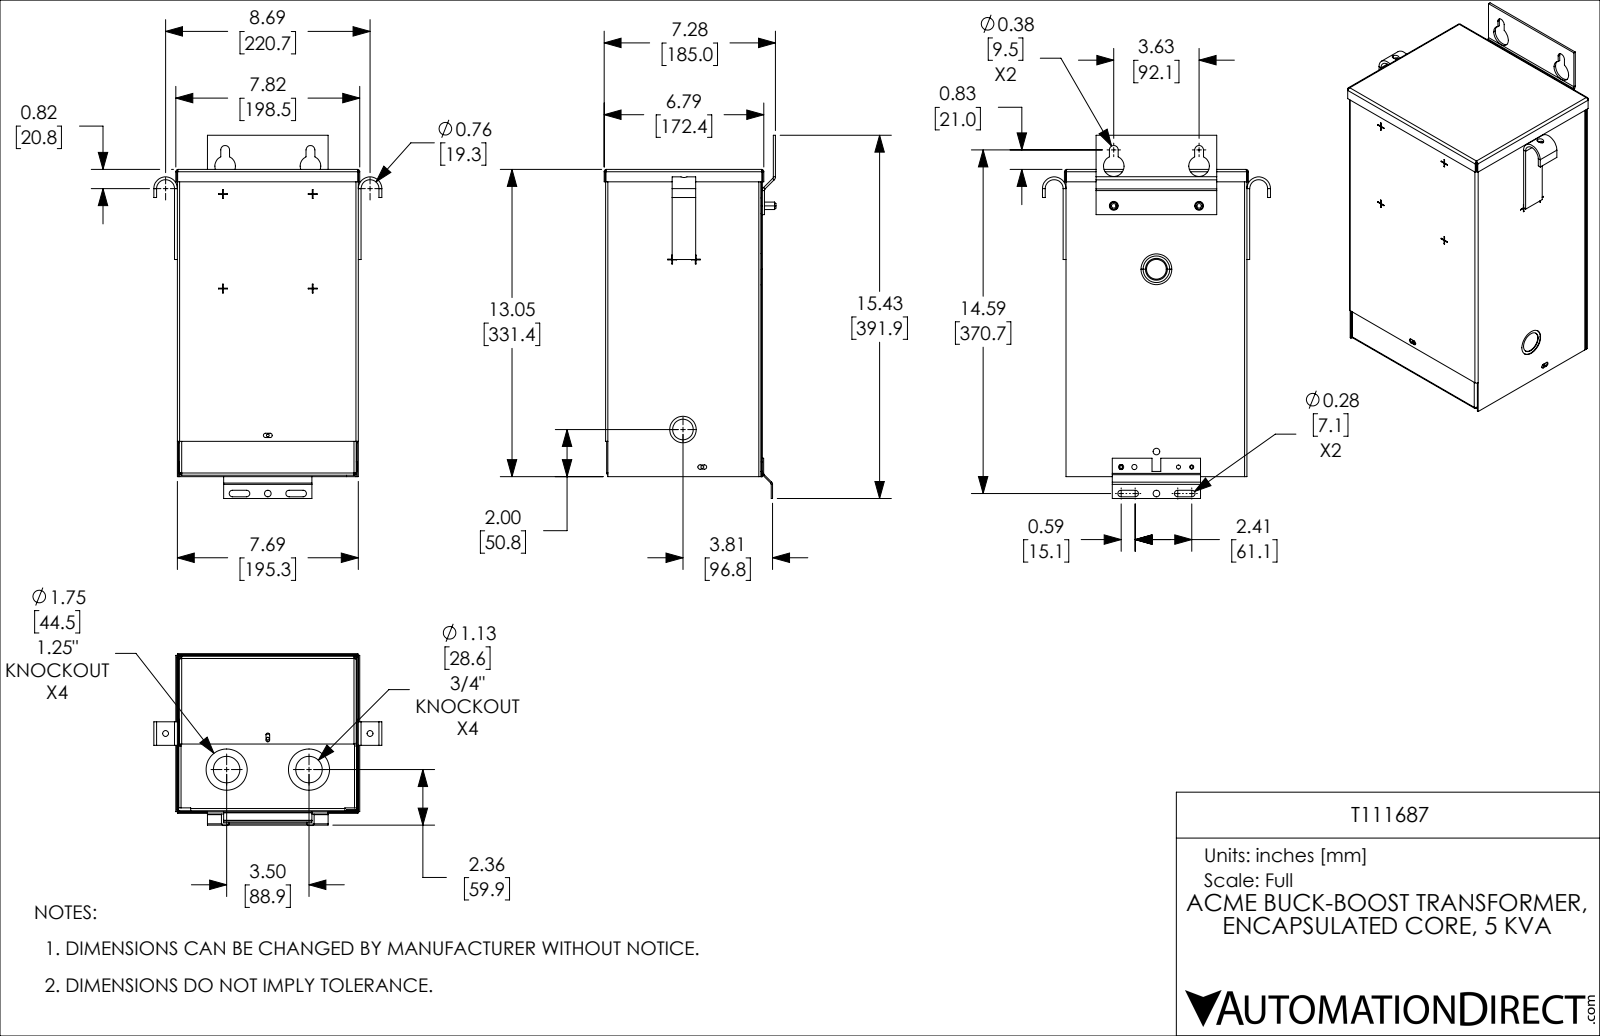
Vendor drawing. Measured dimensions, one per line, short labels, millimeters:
name: T111687
written by: SolidWorks 2021 (CONFIG_CONTROL_DESIGN)
unit: mm
bodies: 10 solids, 520 faces (326 planar, 146 cylindrical, 48 other)
size: 391.89 × 246.13 × 185.43
volume: 446 544 mm³; area: 704 753 mm²
holes: 5× ⌀3.05, 2× ⌀4.37, 2× ⌀5.56, 2× ⌀7.14, 2× ⌀7.94, 2× ⌀9.53, 2× ⌀22.22, 2× ⌀28.58, 2× ⌀44.45, 1× ⌀4.39, 1× ⌀4.76, 1× ⌀22.23
bosses: 2× ⌀7.92
rounds: 16× R1.27, 16× R2.48, 8× R2.38, 4× R3.57, 2× R1.91, 2× R1.98, 2× R2.54, 2× R3.42
face distances: 1.21, 167.95, 194.11, 166.74, 169.16, 195.32, 1.22, 192.9, 1.75, 328.77
hole spacings: 281.89, 324.68, 335.31, 41.61, 47.62, 294.07, 294.08, 14.29
